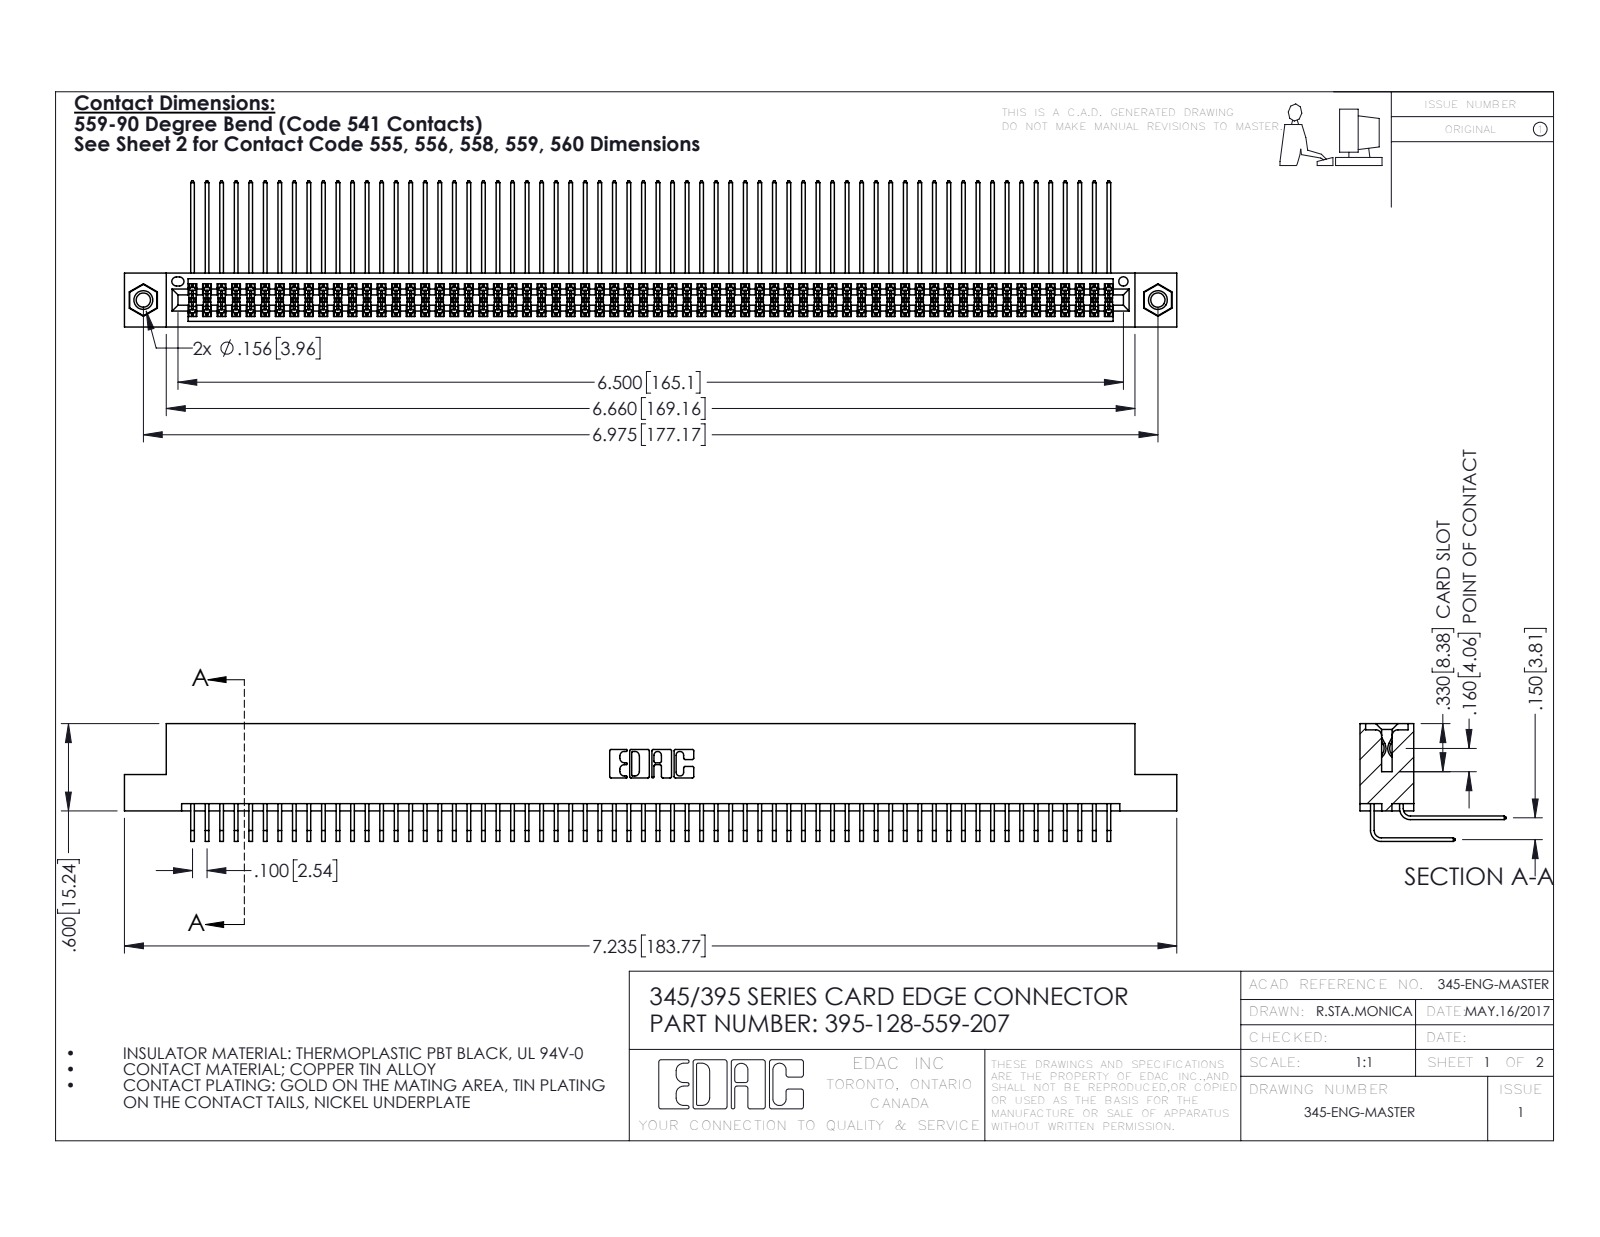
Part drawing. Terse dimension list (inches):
name: 395-128-559-207; 345-292-001_558 559 Tail - 1; 345 Part_Flush Mounting Lugs - 0.156 Dia-TI; 345-250-001_345-250-005-103 (+1 more)
written by: SolidWorks 2016 (CONFIG_CONTROL_DESIGN)
unit: in
bodies: 131 solids, 6842 faces (4592 planar, 2234 cylindrical, 16 other)
size: 7.235 × 1.005 × 0.809
volume: 1.146 in³; area: 49.12 in²
holes: 2× ⌀0.098, 2× ⌀0.125, 2× ⌀0.156, 1× ⌀0.064
bosses: 2× ⌀0.155
rounds: 193× R0.006, 22× R0.01, 6× R0.007, 6× R0.031, 3× R0.026, 2× R0.014, 2× R0.019, 2× R0.022
face distances: 0.072, 0.298, 0.2, 0.37, 0.098, 0.272, 0.025, 0.225, 0.175, 0.15
hole spacings: 0.27, 6.739, 6.975
